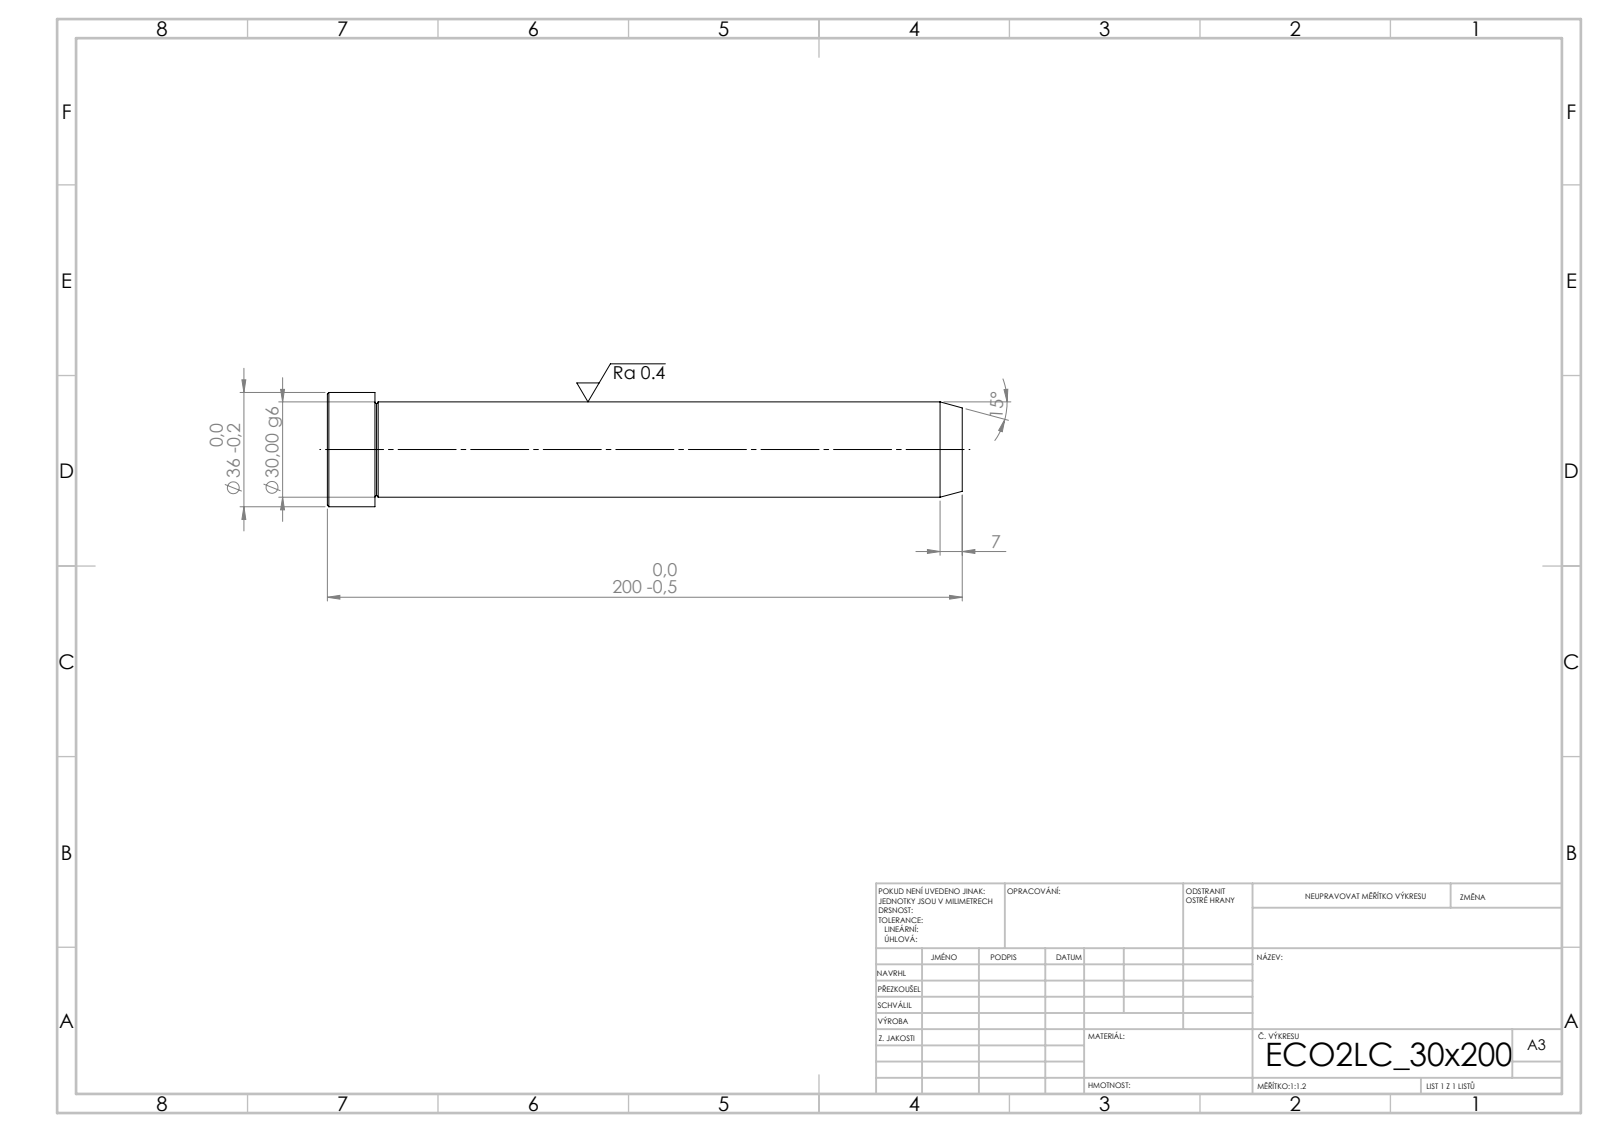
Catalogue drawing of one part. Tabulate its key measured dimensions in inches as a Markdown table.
| quantity | value |
| --- | --- |
| STEP written by | SolidWorks 2019 (CONFIG_CONTROL_DESIGN) |
| units | inches |
| bodies | 1 solid, 15 faces (3 planar, 4 cylindrical, 8 other) |
| overall size | 7.874 × 1.417 × 1.417 |
| volume | 8.872 in³ |
| surface area | 32.55 in² |
| round bosses / shafts (diameter × count) | 1.417 × 1, 1.181 × 1 |
| main face-to-face distances | 7.874, 7.283, 0.591 |
